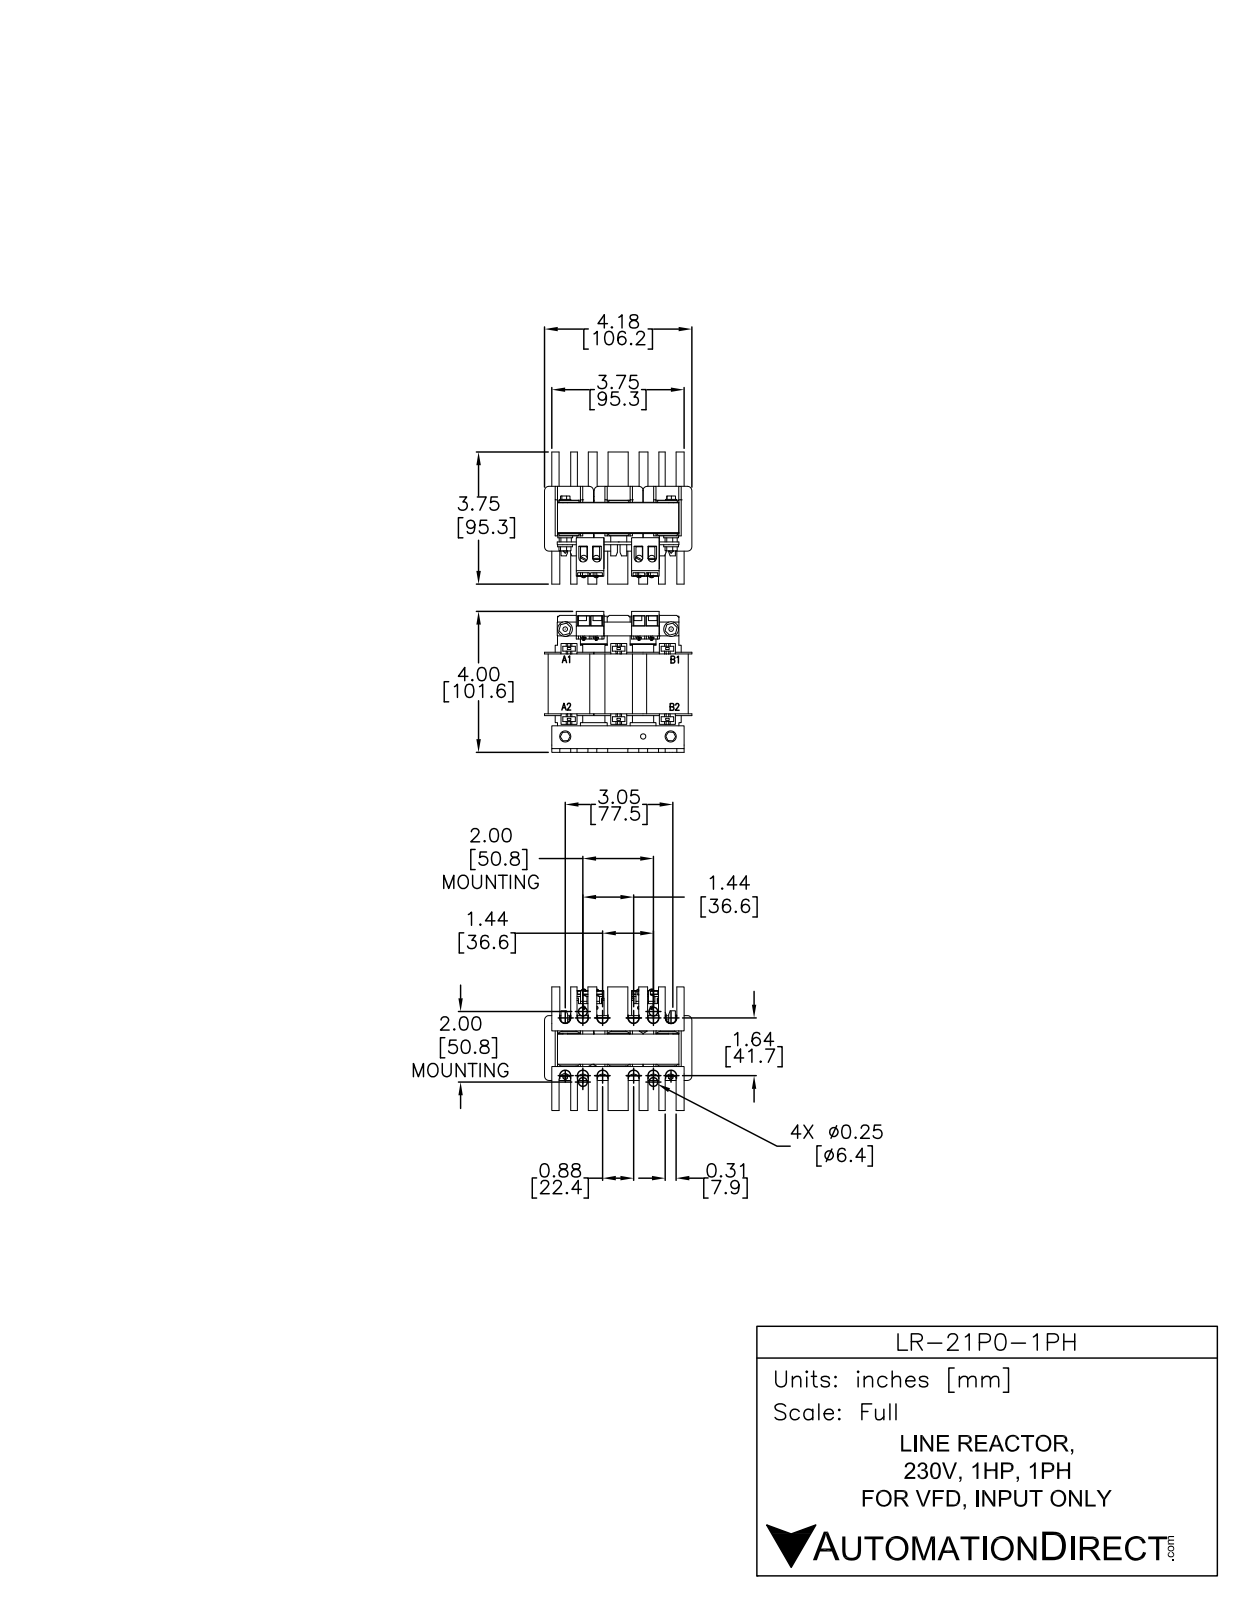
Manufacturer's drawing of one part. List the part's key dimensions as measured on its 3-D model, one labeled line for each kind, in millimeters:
Part name (STEP PRODUCT): LR-21P0-1PH
STEP written by: SolidWorks 2011 (AUTOMOTIVE_DESIGN)
Units: millimetres
Bodies: 17 solids, 1066 faces (846 planar, 220 cylindrical, 0 other)
Overall size (bounding box): 105.25 × 98.41 × 89.25
Volume: 290 384 mm³ · Surface area: 108 495 mm²
Round bosses / shafts (diameter × count): ⌀7.75 ×4, ⌀3.5 ×4
Partial cylindrical surfaces — rounded edges, fillets, slot ends (radius × count): R4 ×42, R1.82 ×24, R8 ×12, R1 ×8, R3 ×4, R0.86 ×3, R1.25 ×2
Main face-to-face distances: 5, 26.25, 2.5, 7.5, 51, 48.5, 43.5, 2.75, 21.5, 29
